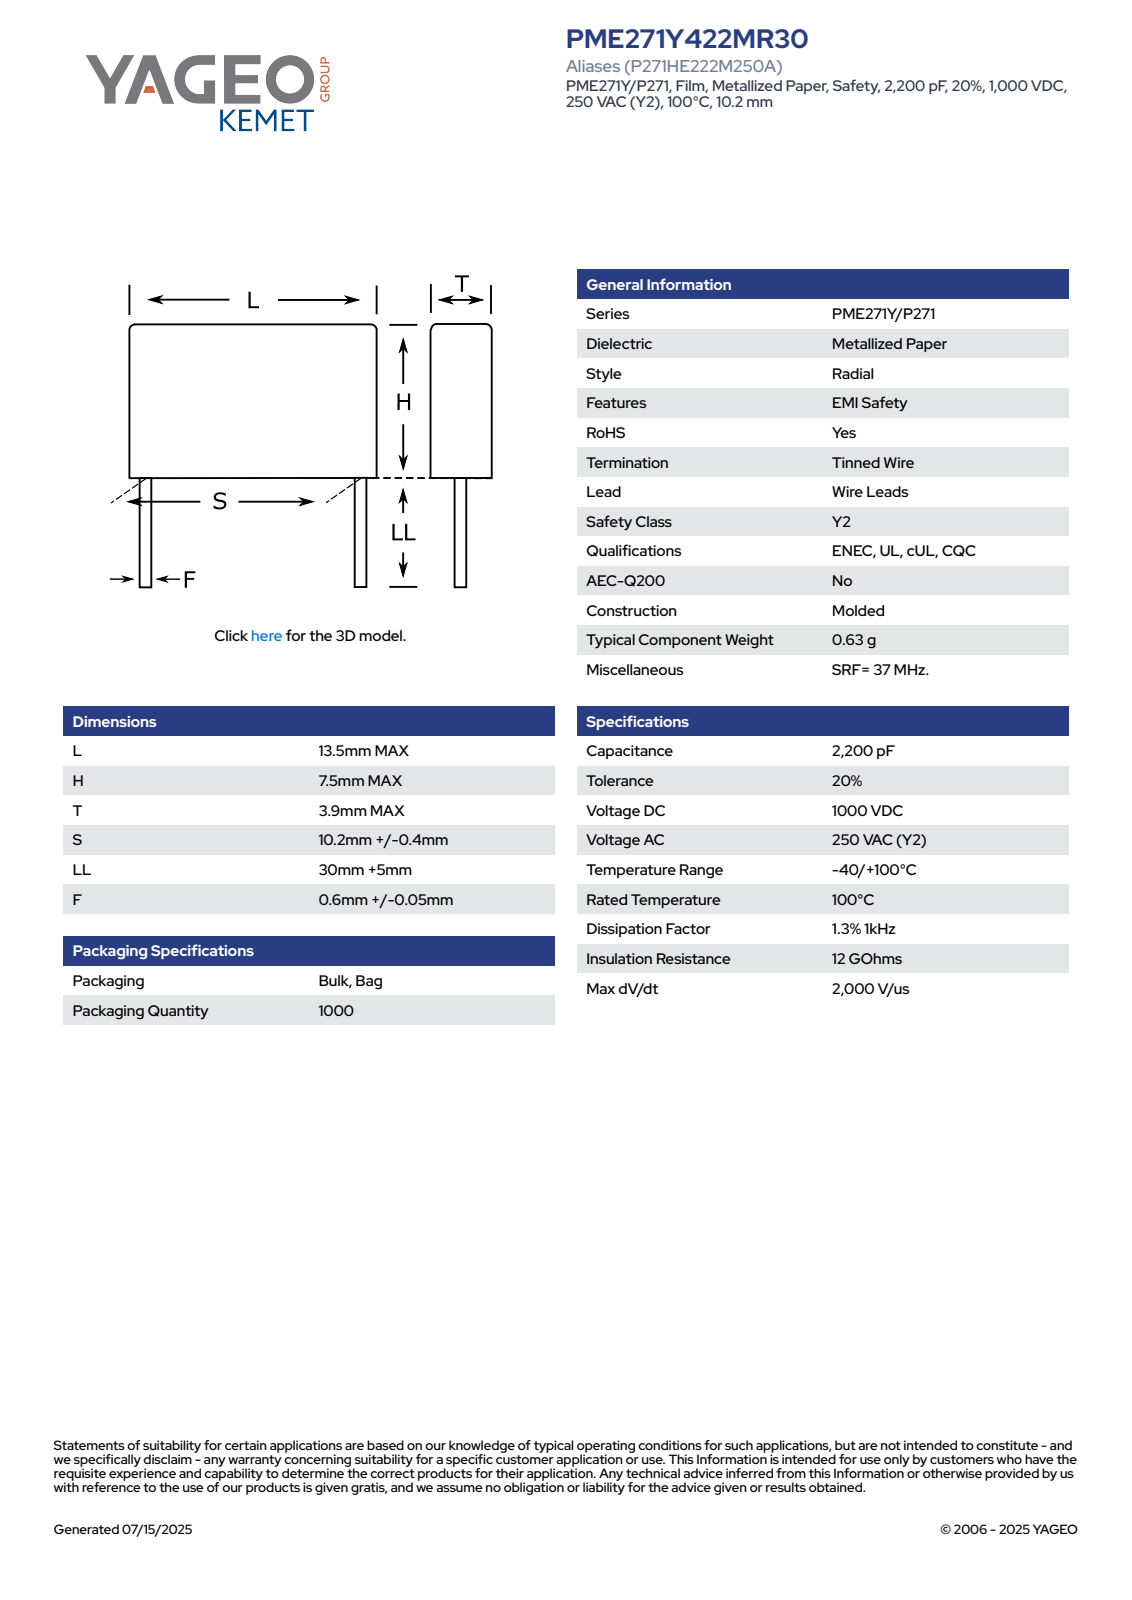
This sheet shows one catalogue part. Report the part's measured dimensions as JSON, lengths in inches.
{"part_name": "CFR_MOLDED_13.5X7.5X3.9_L13.5H7.5T3.9S10.2LL35F0.65", "step_written_by": "SolidWorks 2014 (AUTOMOTIVE_DESIGN)", "units": "inches", "bodies": {"solids": 4, "faces": 73, "planar": 65, "cylindrical": 8, "other": 0}, "overall_size": [1.673, 0.531, 0.154], "volume_in3": 0.025, "surface_area_in2": 0.791, "round_bosses_or_shafts": [[0.026, 2]], "partial_cylinders_radius": [[0.02, 4]], "face_to_face_distances": [0.154, 0.295, 0.531, 1.378, 1.673, 0.048, 1.549, 0.171, 0.124, 1.502]}
